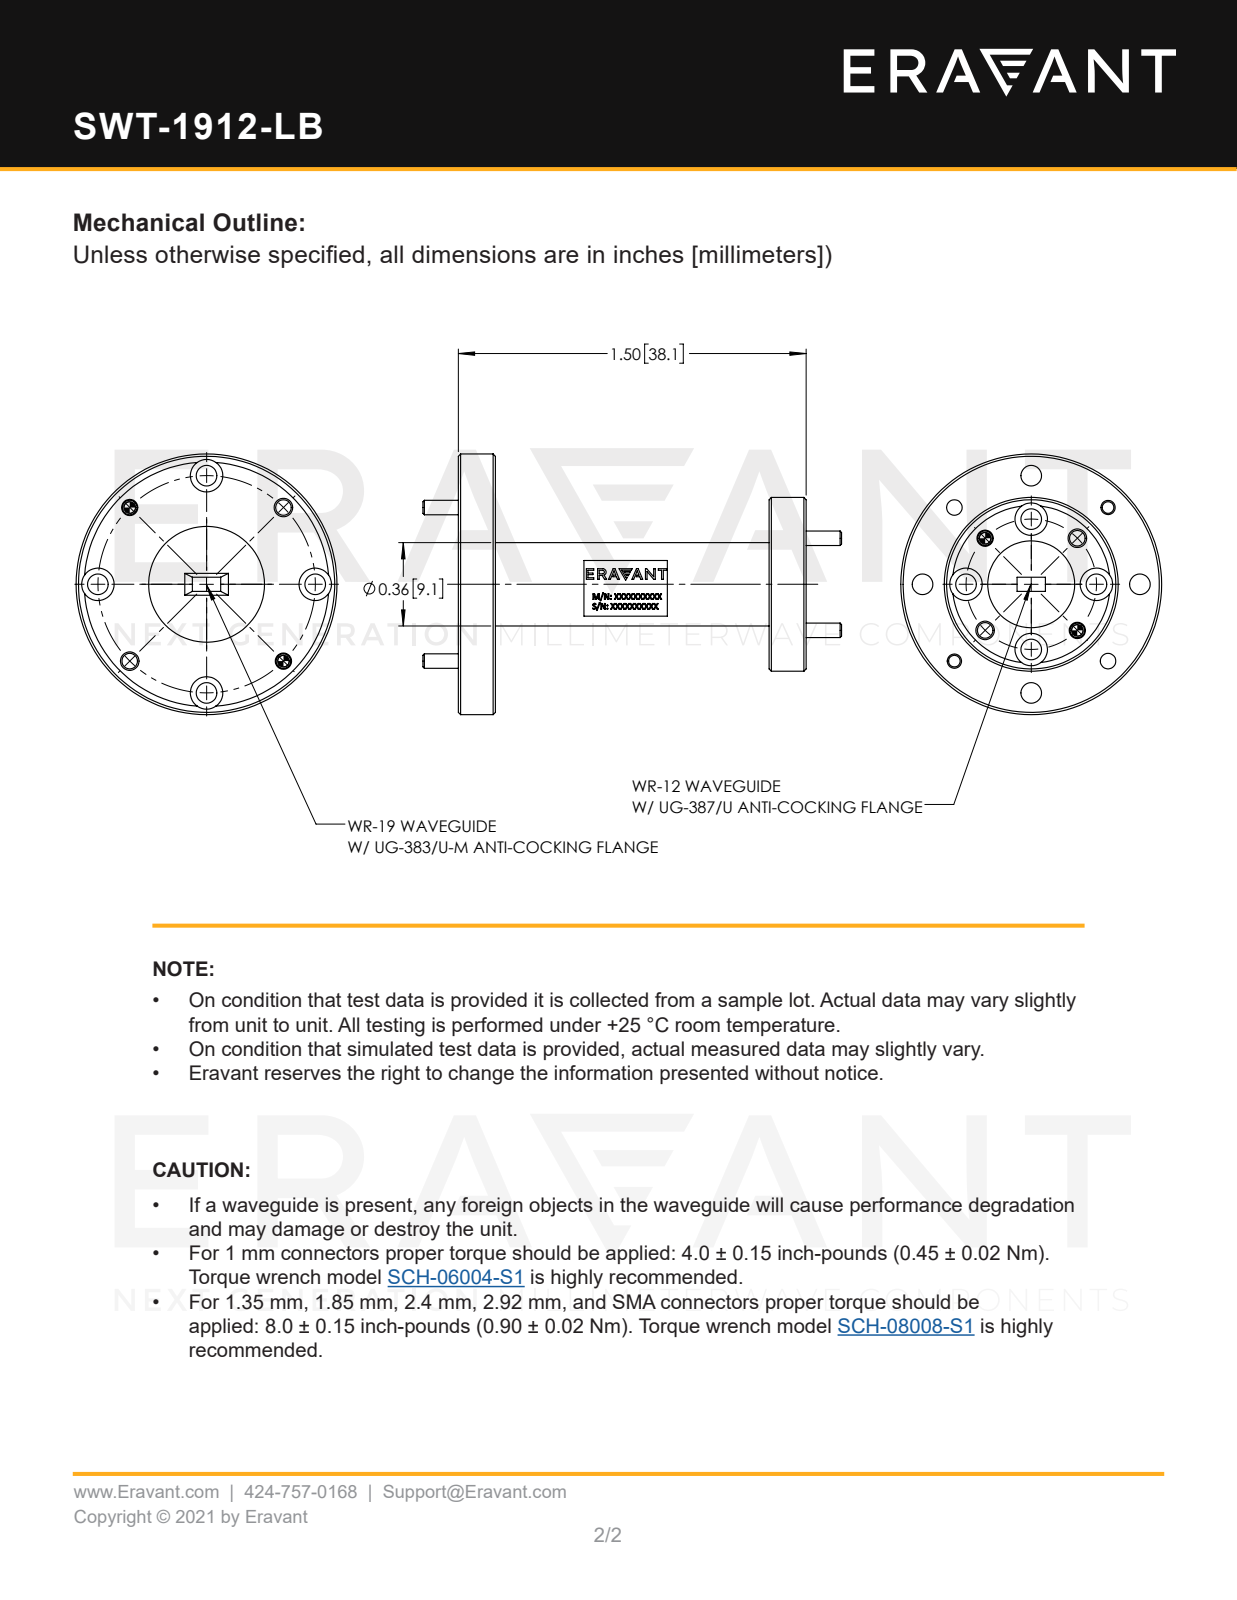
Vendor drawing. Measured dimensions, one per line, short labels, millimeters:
name: SWT-1912-LB
written by: SolidWorks 2021 (CONFIG_CONTROL_DESIGN)
unit: mm
bodies: 5 solids, 148 faces (34 planar, 74 cylindrical, 40 other)
size: 45.8 × 28.6 × 28.6
volume: 5 260 mm³; area: 3 708 mm²
holes: 8× ⌀2.3, 8× ⌀3.6, 4× ⌀1.5, 4× ⌀1.7, 1× ⌀17.3, 1× ⌀26.8
bosses: 4× ⌀1.6, 1× ⌀28.6, 1× ⌀19.1, 1× ⌀12.7, 1× ⌀9.5, 1× ⌀9.1
face distances: 3.6, 33.5, 30, 34, 4.1, 0.5, 37.1, 37.6, 37.6, 0.5
hole spacings: 8.5, 13.9, 5.5, 9.1, 10.1, 16.8, 17.7, 17.7
